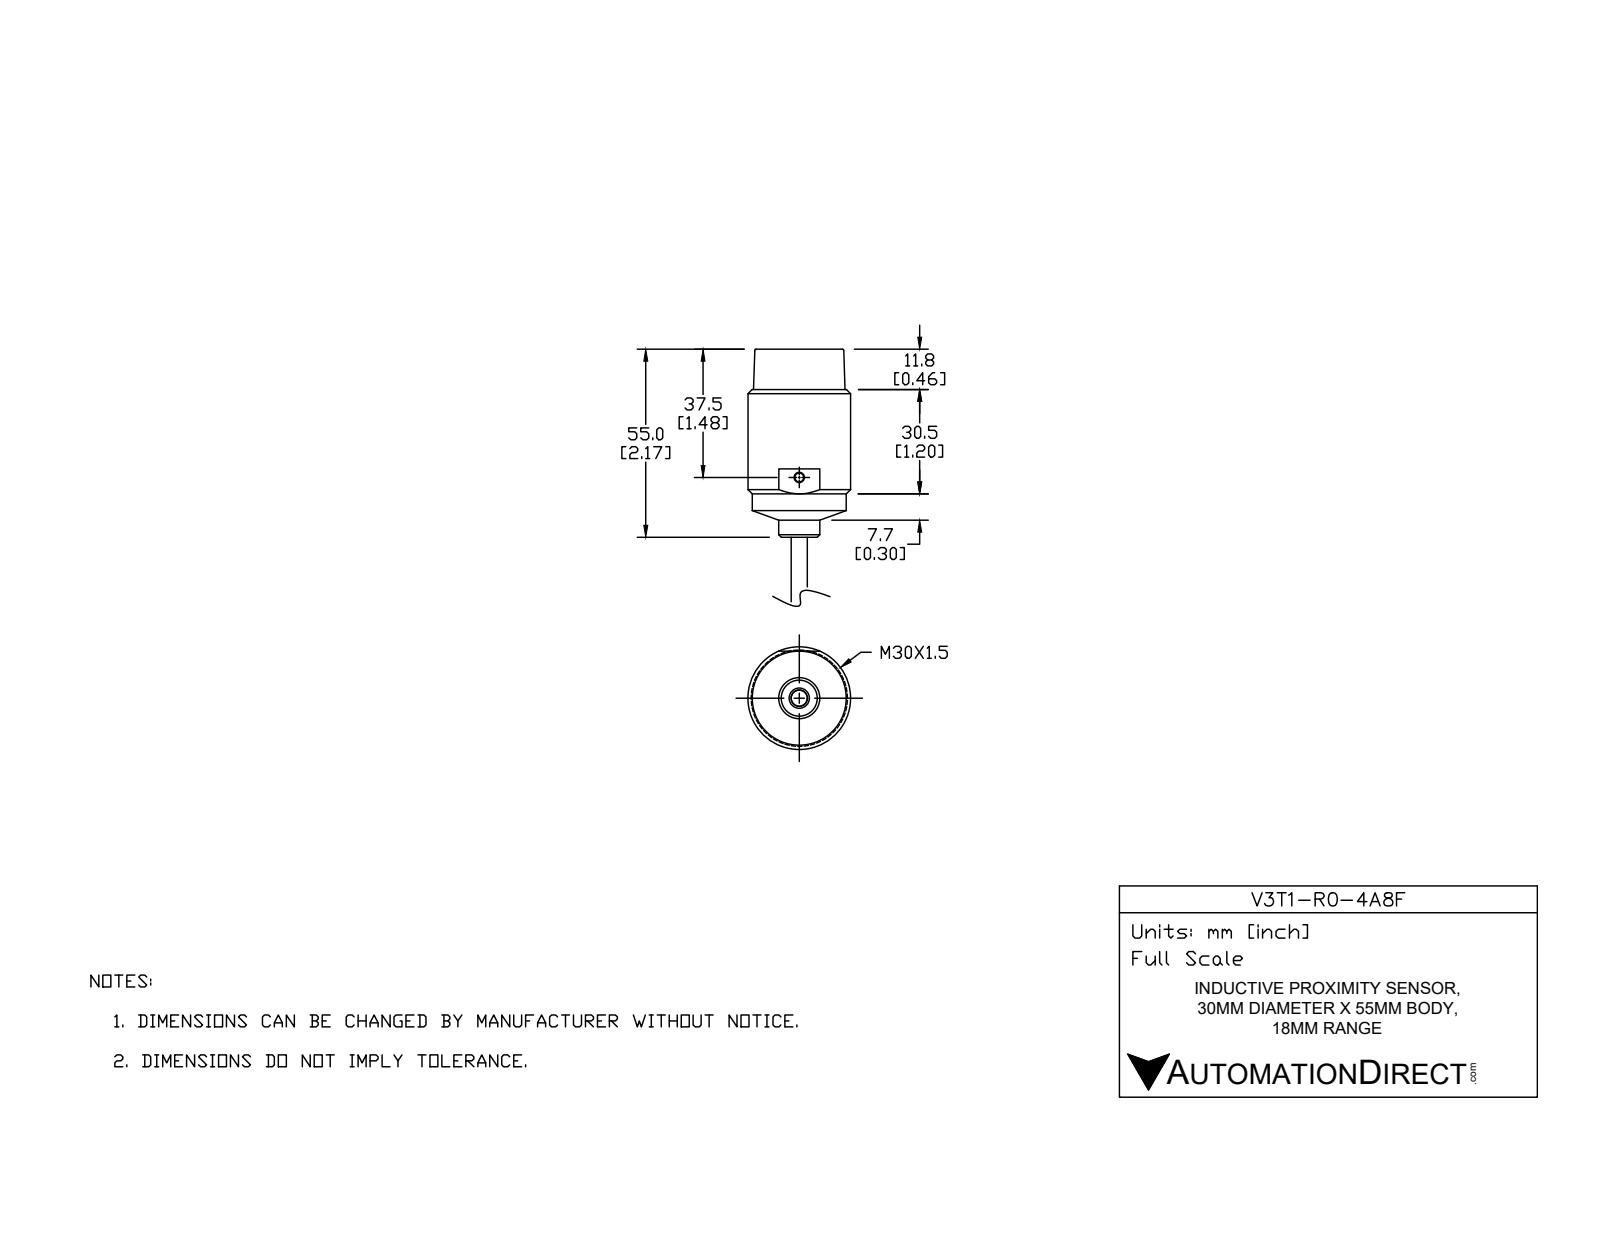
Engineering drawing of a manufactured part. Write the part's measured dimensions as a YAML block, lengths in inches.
part_name: "V3T1_4A_fig"
step_written_by: "ST-DEVELOPER v16.7 (AUTOMOTIVE_DESIGN)"
units: inches
bodies: {solids: 1, faces: 24, planar: 9, cylindrical: 6, other: 9}
overall_size: [3.681, 1.181, 1.181]
volume: 2
surface_area: 11.47
round_holes:
  - {diameter: 0.102, count: 1}
round_bosses_or_shafts:
  - {diameter: 1.181, count: 1}
  - {diameter: 1.083, count: 1}
  - {diameter: 0.472, count: 1}
  - {diameter: 0.185, count: 1}
partial_cylinders:
  - {radius: 0.524, count: 1}
face_to_face_distances: [0.472, 0.476, 2.165, 1.693, 1.689, 0.465, 1.701, 3.681, 3.217, 3.209]
